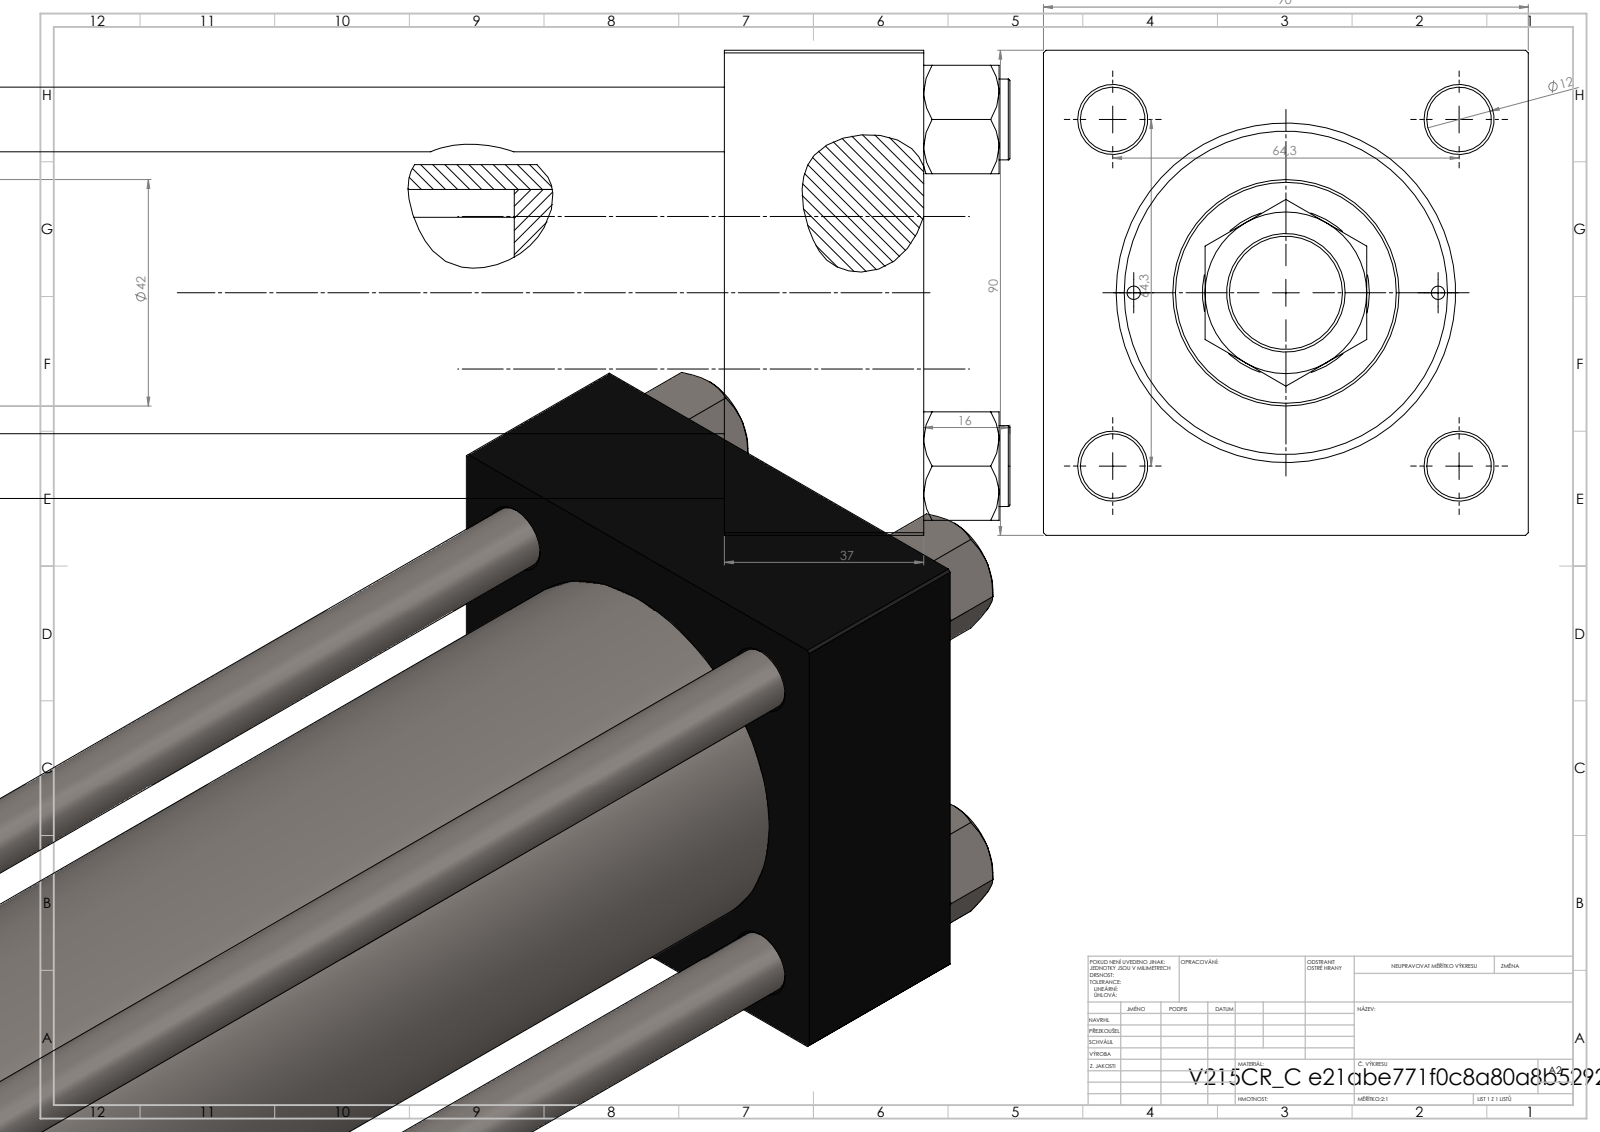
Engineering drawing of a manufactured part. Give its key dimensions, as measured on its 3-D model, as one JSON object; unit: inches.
{"part_name": "V215_VC_A; V215CR_C_TYCINKA; NUT_M5_C; MFA (+2 more)", "step_written_by": "SolidWorks 2019 (CONFIG_CONTROL_DESIGN)", "units": "inches", "bodies": {"solids": 12, "faces": 1206, "planar": 544, "cylindrical": 94, "other": 568}, "overall_size": [22.756, 3.543, 3.543], "volume_in3": 93.31, "surface_area_in2": 620.7, "round_holes": [[0.472, 4], [0.098, 2], [0.276, 2], [0.825, 2], [1.181, 2], [0.728, 1], [1.102, 1], [1.22, 1], [1.969, 1], [2.362, 1], [2.48, 1]], "round_bosses_or_shafts": [[0.591, 4], [2.717, 1], [1.654, 1], [0.866, 1], [0.551, 1]], "partial_cylinders_radius": [[0.531, 1]], "face_to_face_distances": [3.543, 1.457, 19.094, 17.638, 16.772, 15.315, 2.323, 17.965, 16.508, 1.193], "hole_center_spacings": [1.275, 1.79, 2.531, 2.694, 1.112, 3.58, 2.224, 16.831]}
